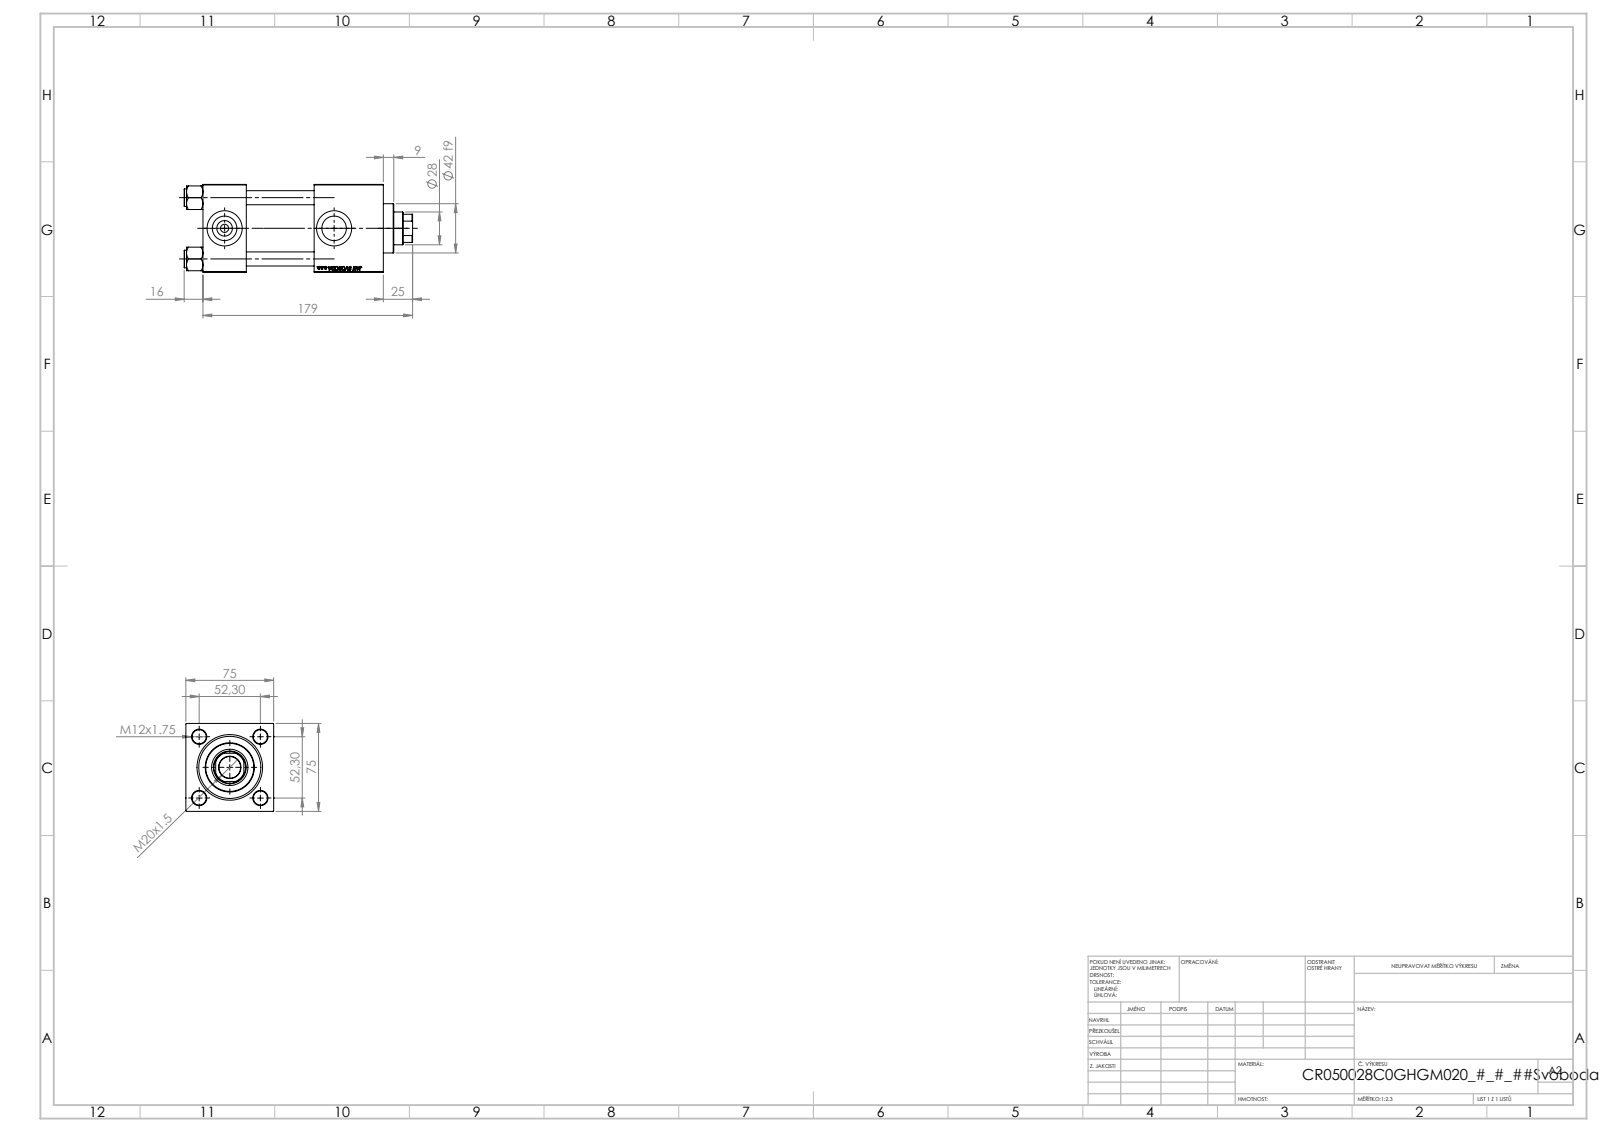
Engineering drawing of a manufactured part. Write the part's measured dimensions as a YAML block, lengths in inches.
part_name: "V215CR_C_TYCINKA; V215_VC_A; V215CR_VCP_C; V215CR_C_Body (+1 more)"
step_written_by: "SolidWorks 2019 (CONFIG_CONTROL_DESIGN)"
units: inches
bodies: {solids: 11, faces: 1148, planar: 526, cylindrical: 86, other: 536}
overall_size: [7.677, 2.974, 2.953]
volume: 40.83
surface_area: 233.9
round_holes:
  - {diameter: 0.472, count: 4}
  - {diameter: 0.276, count: 2}
  - {diameter: 0.825, count: 2}
  - {diameter: 1.181, count: 2}
  - {diameter: 0.728, count: 1}
  - {diameter: 1.102, count: 1}
  - {diameter: 1.22, count: 1}
  - {diameter: 1.614, count: 1}
  - {diameter: 1.969, count: 1}
  - {diameter: 2.087, count: 1}
round_bosses_or_shafts:
  - {diameter: 0.591, count: 4}
  - {diameter: 2.205, count: 1}
  - {diameter: 1.654, count: 1}
partial_cylinders:
  - {radius: 0.531, count: 1}
face_to_face_distances: [2.953, 1.457, 6.063, 4.606, 3.74, 2.283, 2.323, 4.933, 3.476, 1.193]
hole_center_spacings: [1.456, 2.059, 2.912, 3.681]
